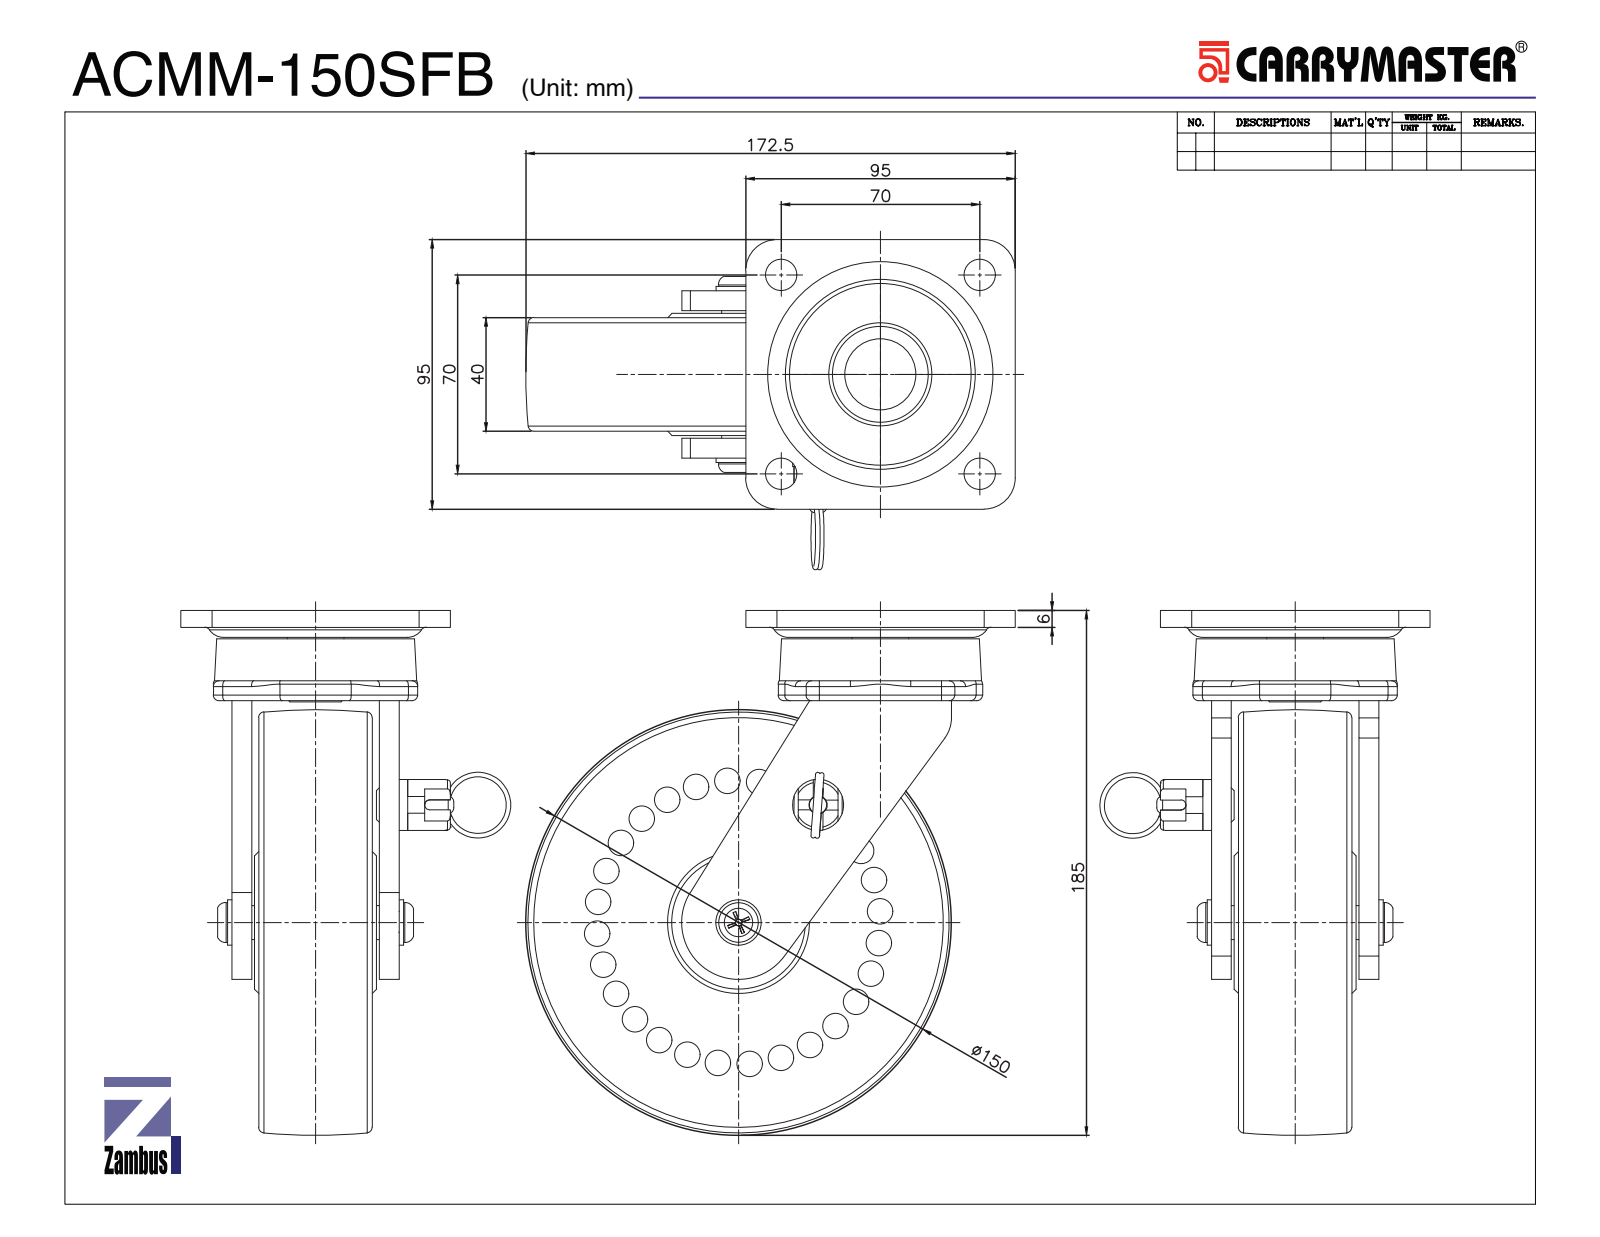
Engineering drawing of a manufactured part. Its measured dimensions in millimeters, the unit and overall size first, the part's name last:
Units: millimetres
Overall size (bounding box): 185 × 172.5 × 116.33
Round holes (diameter × count): ⌀9 ×28, ⌀11 ×4, ⌀3 ×1, ⌀6.4 ×1, ⌀6.8 ×1, ⌀8.7 ×1, ⌀12 ×1, ⌀12.3 ×1, ⌀14.5 ×1, ⌀17.5 ×1, ⌀26.5 ×1, ⌀31.1 ×1
Round bosses / shafts (diameter × count): ⌀38 ×1, ⌀25 ×1, ⌀20 ×1, ⌀18 ×1, ⌀16 ×1, ⌀14 ×1, ⌀12.17 ×1, ⌀12 ×1
Partial cylindrical surfaces — rounded edges, fillets, slot ends (radius × count): R2 ×12, R5 ×4, R11 ×4, R1.75 ×2, R12 ×1, R14.5 ×1, R20 ×1, R36 ×1
Main face-to-face distances: 40, 9.5, 2.5, 49.5, 7, 52, 42.5, 45, 59, 6
Hole centre spacings: 50, 62.35, 99.37, 33.03, 43.39, 22.25, 11.2, 94.39
Volume: 861 632 mm³ · Surface area: 135 545 mm²
Bodies: 13 solids, 572 faces (184 planar, 211 cylindrical, 177 other)
Part name (STEP PRODUCT): ACMM-150SFB ASSY
STEP written by: SolidWorks 2016 (CONFIG_CONTROL_DESIGN)
